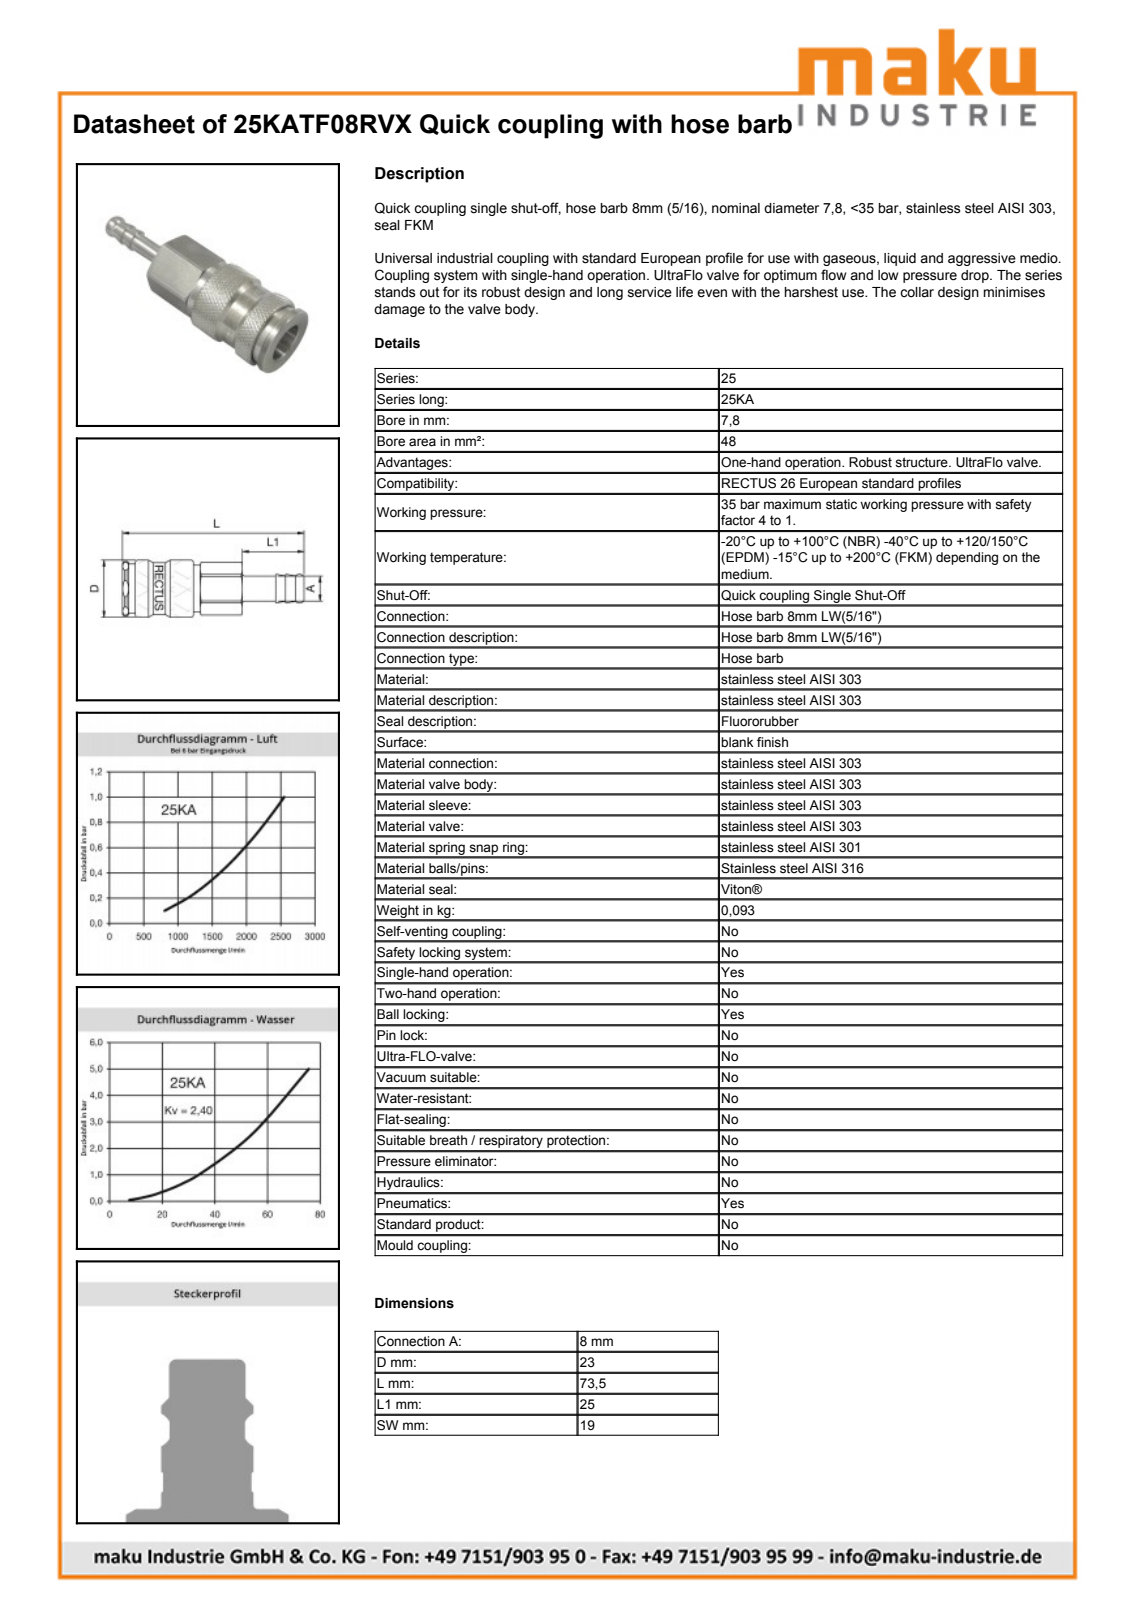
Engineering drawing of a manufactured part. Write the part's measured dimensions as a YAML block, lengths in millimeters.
part_name: "D108218"
step_written_by: "Autodesk Inventor 2013 (AUTOMOTIVE_DESIGN)"
units: millimeters
bodies: {solids: 2, faces: 618, planar: 213, cylindrical: 85, other: 320}
overall_size: [73.5, 23.15, 23.15]
volume: 17248
surface_area: 8291
round_holes:
  - {diameter: 15.1, count: 1}
  - {diameter: 16, count: 1}
  - {diameter: 17.25, count: 1}
  - {diameter: 19.35, count: 1}
  - {diameter: 20.05, count: 1}
round_bosses_or_shafts:
  - {diameter: 23.15, count: 1}
  - {diameter: 21, count: 1}
  - {diameter: 20, count: 1}
  - {diameter: 18.95, count: 1}
  - {diameter: 15.3, count: 1}
  - {diameter: 15, count: 1}
  - {diameter: 14.79, count: 1}
  - {diameter: 8.1, count: 1}
partial_cylinders:
  - {radius: 10.4, count: 1}
  - {radius: 10.7, count: 1}
  - {radius: 11, count: 1}
face_to_face_distances: [19, 48.5, 24.5, 24, 5.25, 19.25, 28.75, 4.25, 19.75, 73.5]
